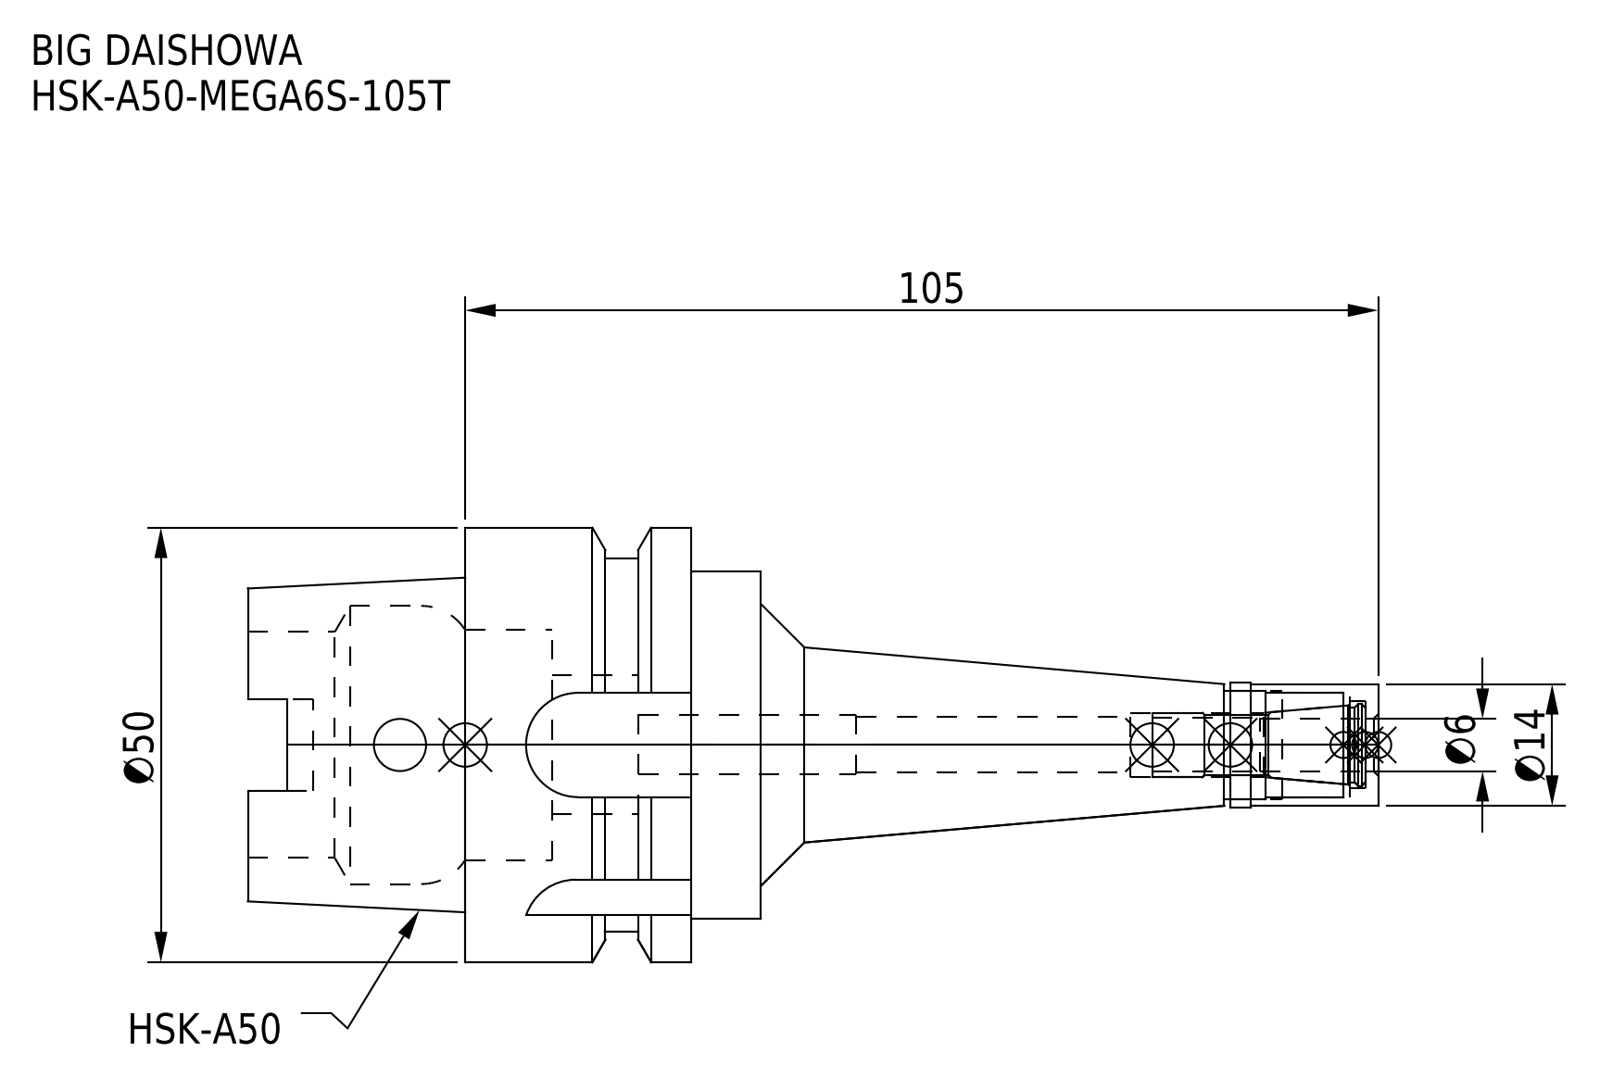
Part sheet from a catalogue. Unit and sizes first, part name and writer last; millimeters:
Units: millimetres
Overall size (bounding box): 130 × 50 × 50
Round holes (diameter × count): ⌀6 ×1, ⌀6.1 ×1, ⌀6.4 ×1, ⌀6.8 ×1, ⌀7.4 ×1, ⌀10 ×1, ⌀12 ×1, ⌀12.5 ×1, ⌀16 ×1, ⌀26 ×1, ⌀26.6 ×1, ⌀32 ×1
Round bosses / shafts (diameter × count): ⌀50 ×1, ⌀43 ×1, ⌀40 ×1, ⌀14.3 ×1, ⌀14 ×1, ⌀12.98 ×1
Partial cylindrical surfaces — rounded edges, fillets, slot ends (radius × count): R2.38 ×4, R6 ×4
Main face-to-face distances: 26, 8, 34, 24.05, 16.05, 9.95, 59, 51, 34.95, 25
Volume: 74 501 mm³ · Surface area: 22 629 mm²
Bodies: 2 solids, 122 faces (47 planar, 53 cylindrical, 22 other)
Part name (STEP PRODUCT): HSK-A50-MEGA6S-105T_060.stp; DXF_TEMP_ASSY_ASM_4_ASM.stp; HSK-A50-MEGA6S-105T; HSK-A50-MEGA6S-105T_060-FreeParts (+3 more)
STEP written by: SolidWorks 2019 (CONFIG_CONTROL_DESIGN)
